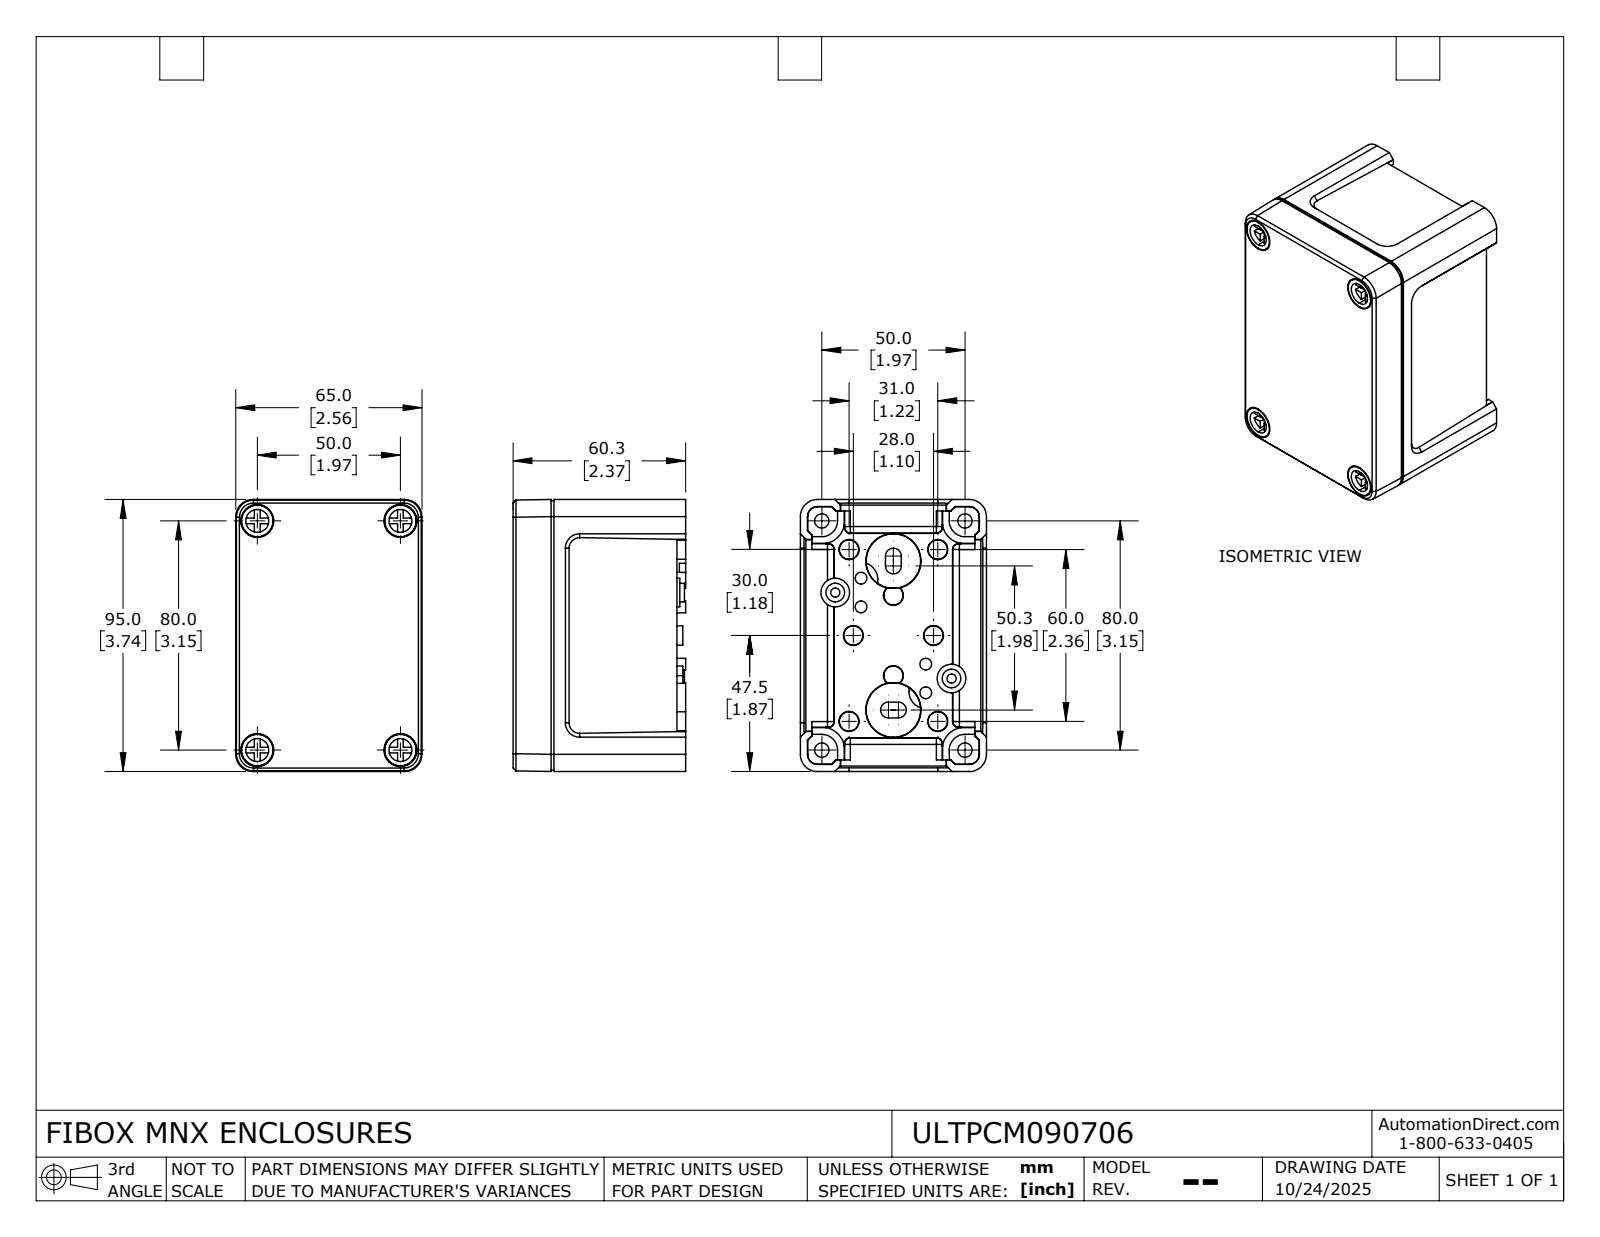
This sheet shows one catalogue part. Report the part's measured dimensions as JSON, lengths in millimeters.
{"part_name": "ULTPCM090706_Default", "step_written_by": "SolidWorks 2024 (CONFIG_CONTROL_DESIGN)", "units": "millimeters", "bodies": {"solids": 6, "faces": 593, "planar": 318, "cylindrical": 175, "other": 100}, "overall_size": [95, 65, 60.2], "volume_mm3": 100200, "surface_area_mm2": 75940, "round_holes": [[3.2, 10], [5, 4], [8, 4]], "round_bosses_or_shafts": [[11, 4], [7.2, 4], [4.1, 4], [10, 2], [6.5, 2]], "partial_cylinders_radius": [[2, 24], [6, 10], [0.5, 8], [1, 8], [2.3, 4], [2.6, 4], [2.7, 4], [5, 4]], "face_to_face_distances": [1.8, 2, 2.7, 5, 50.2, 10.5, 13.3, 37, 3, 47.5], "hole_center_spacings": [13.8, 19.8, 22.3, 30, 36.1, 41.5, 41.7, 42.1]}
